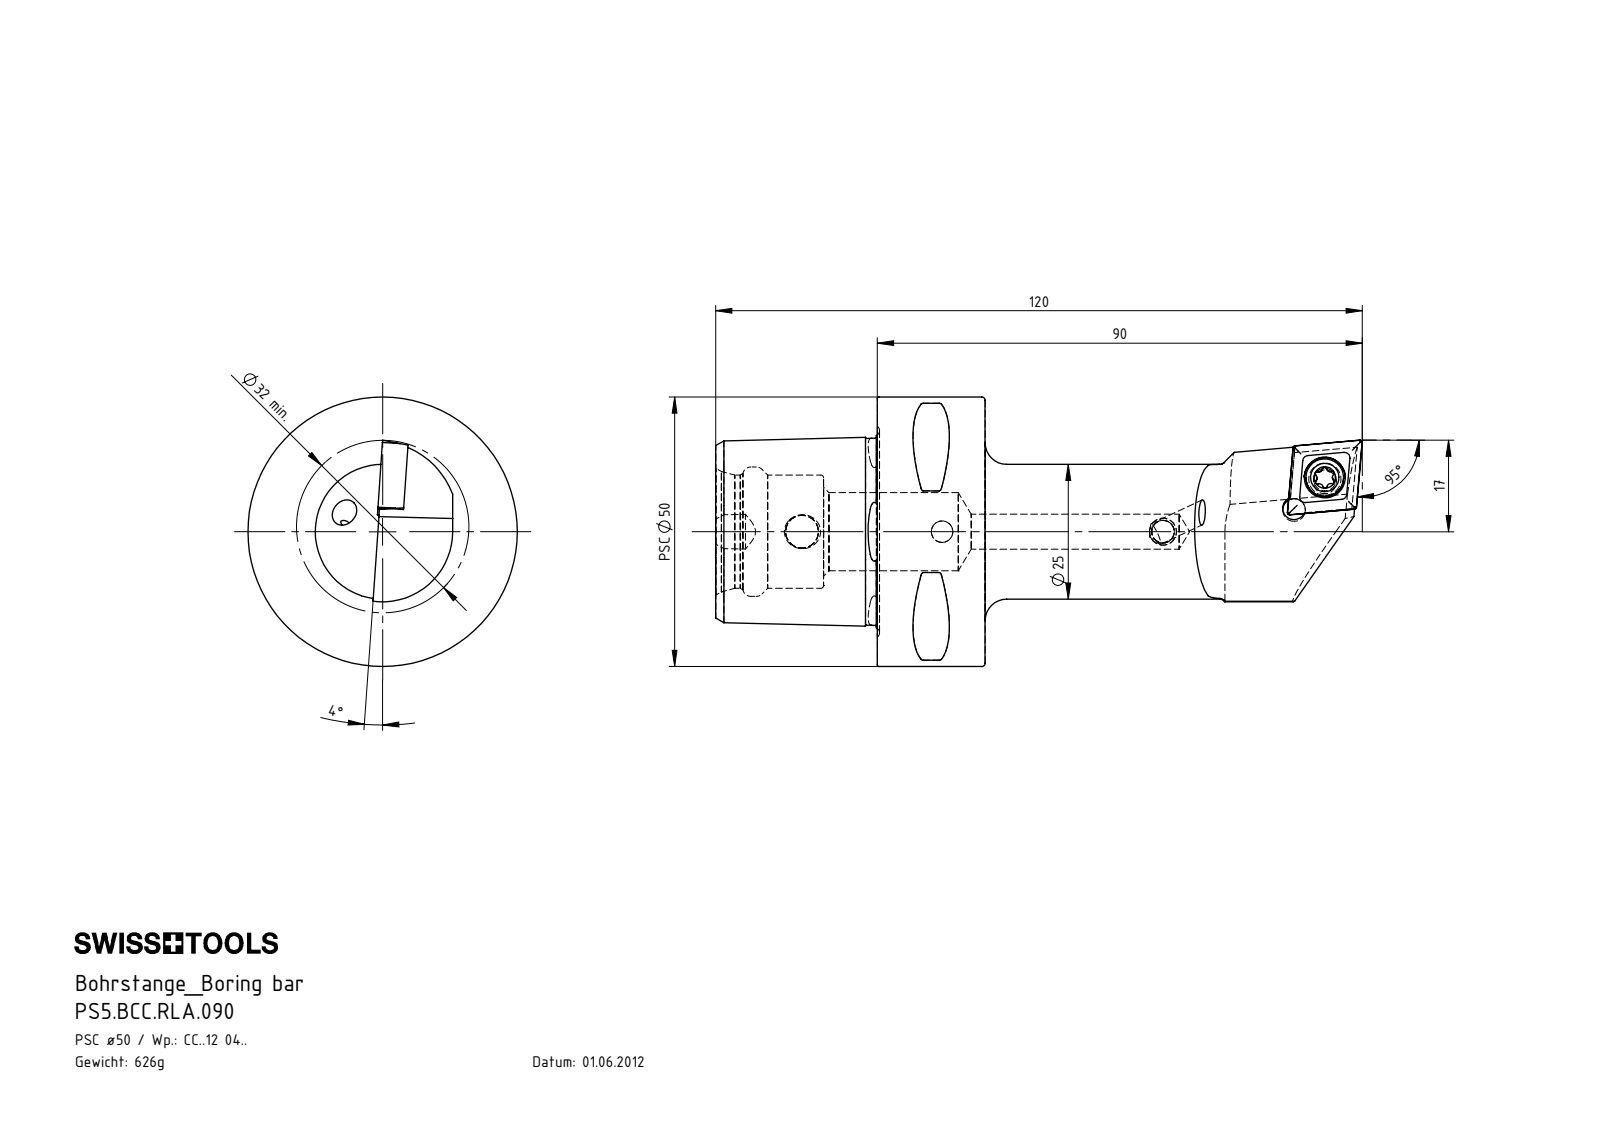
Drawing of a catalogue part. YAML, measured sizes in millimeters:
part_name: "PS5.BCC.RLA.090; CCMT120404; WCC-ER2.001.010_A; KVT_MB_600_050 (+1 more)"
step_written_by: "SolidWorks 2017 (AUTOMOTIVE_DESIGN)"
units: millimeters
bodies: {solids: 5, faces: 278, planar: 49, cylindrical: 74, other: 155}
overall_size: [120, 50, 50]
volume: 79797
surface_area: 19993
round_holes:
  - {diameter: 4.2, count: 4}
  - {diameter: 4, count: 2}
  - {diameter: 5.5, count: 1}
  - {diameter: 6.1, count: 1}
  - {diameter: 6.5, count: 1}
  - {diameter: 7.6, count: 1}
  - {diameter: 14.5, count: 1}
  - {diameter: 21, count: 1}
  - {diameter: 24, count: 1}
round_bosses_or_shafts:
  - {diameter: 5, count: 2}
  - {diameter: 50, count: 1}
  - {diameter: 25, count: 1}
  - {diameter: 7, count: 1}
partial_cylinders:
  - {radius: 0.5, count: 8}
  - {radius: 0.39, count: 6}
  - {radius: 0.69, count: 3}
  - {radius: 0.69, count: 3}
  - {radius: 3, count: 1}
  - {radius: 4, count: 1}
  - {radius: 13, count: 1}
  - {radius: 15, count: 1}
face_to_face_distances: [20, 30, 50, 4.45, 19.18, 44.4, 10, 29.8, 9.8, 20.2]
hole_center_spacings: [8.09, 26, 41, 67]
